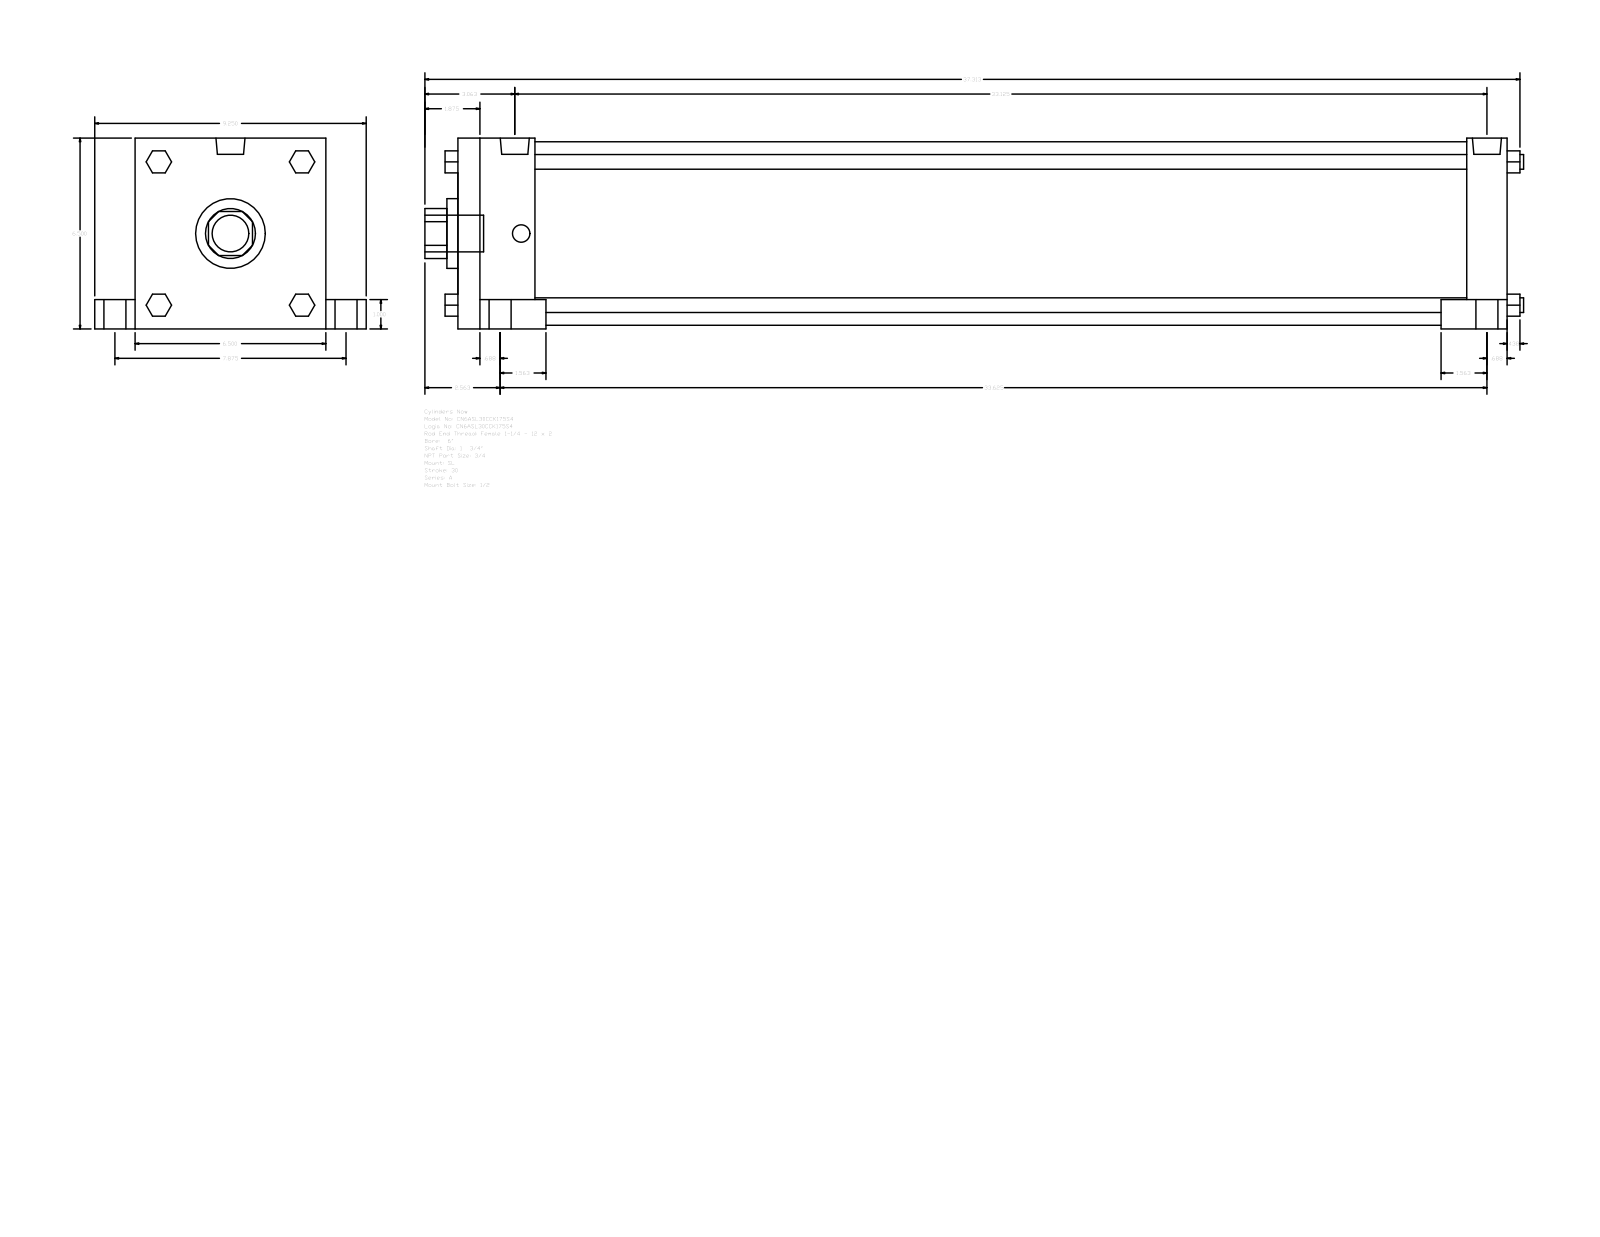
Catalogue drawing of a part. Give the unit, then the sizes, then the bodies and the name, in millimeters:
Units: millimetres
Overall size (bounding box): 950.91 × 234.95 × 165.1
Round holes (diameter × count): ⌀44.45 ×1, ⌀60.33 ×1, ⌀158.75 ×1
Round bosses / shafts (diameter × count): ⌀25.4 ×4, ⌀19.05 ×4, ⌀15.08 ×4, ⌀12.7 ×4, ⌀25.12 ×2, ⌀31.75 ×1
Partial cylindrical surfaces — rounded edges, fillets, slot ends (radius × count): R21.63 ×1
Main face-to-face distances: 165.1, 908.05, 34.92, 66.68, 841.37, 873.13, 806.45, 25.4, 139.7, 200.02
Bodies: 0 solids, 150 faces (114 planar, 36 cylindrical, 0 other)
Part name (STEP PRODUCT): A_SL__0600_1.75
STEP written by: GSSL Pune (CONFIG_CONTROL_DESIGN)
